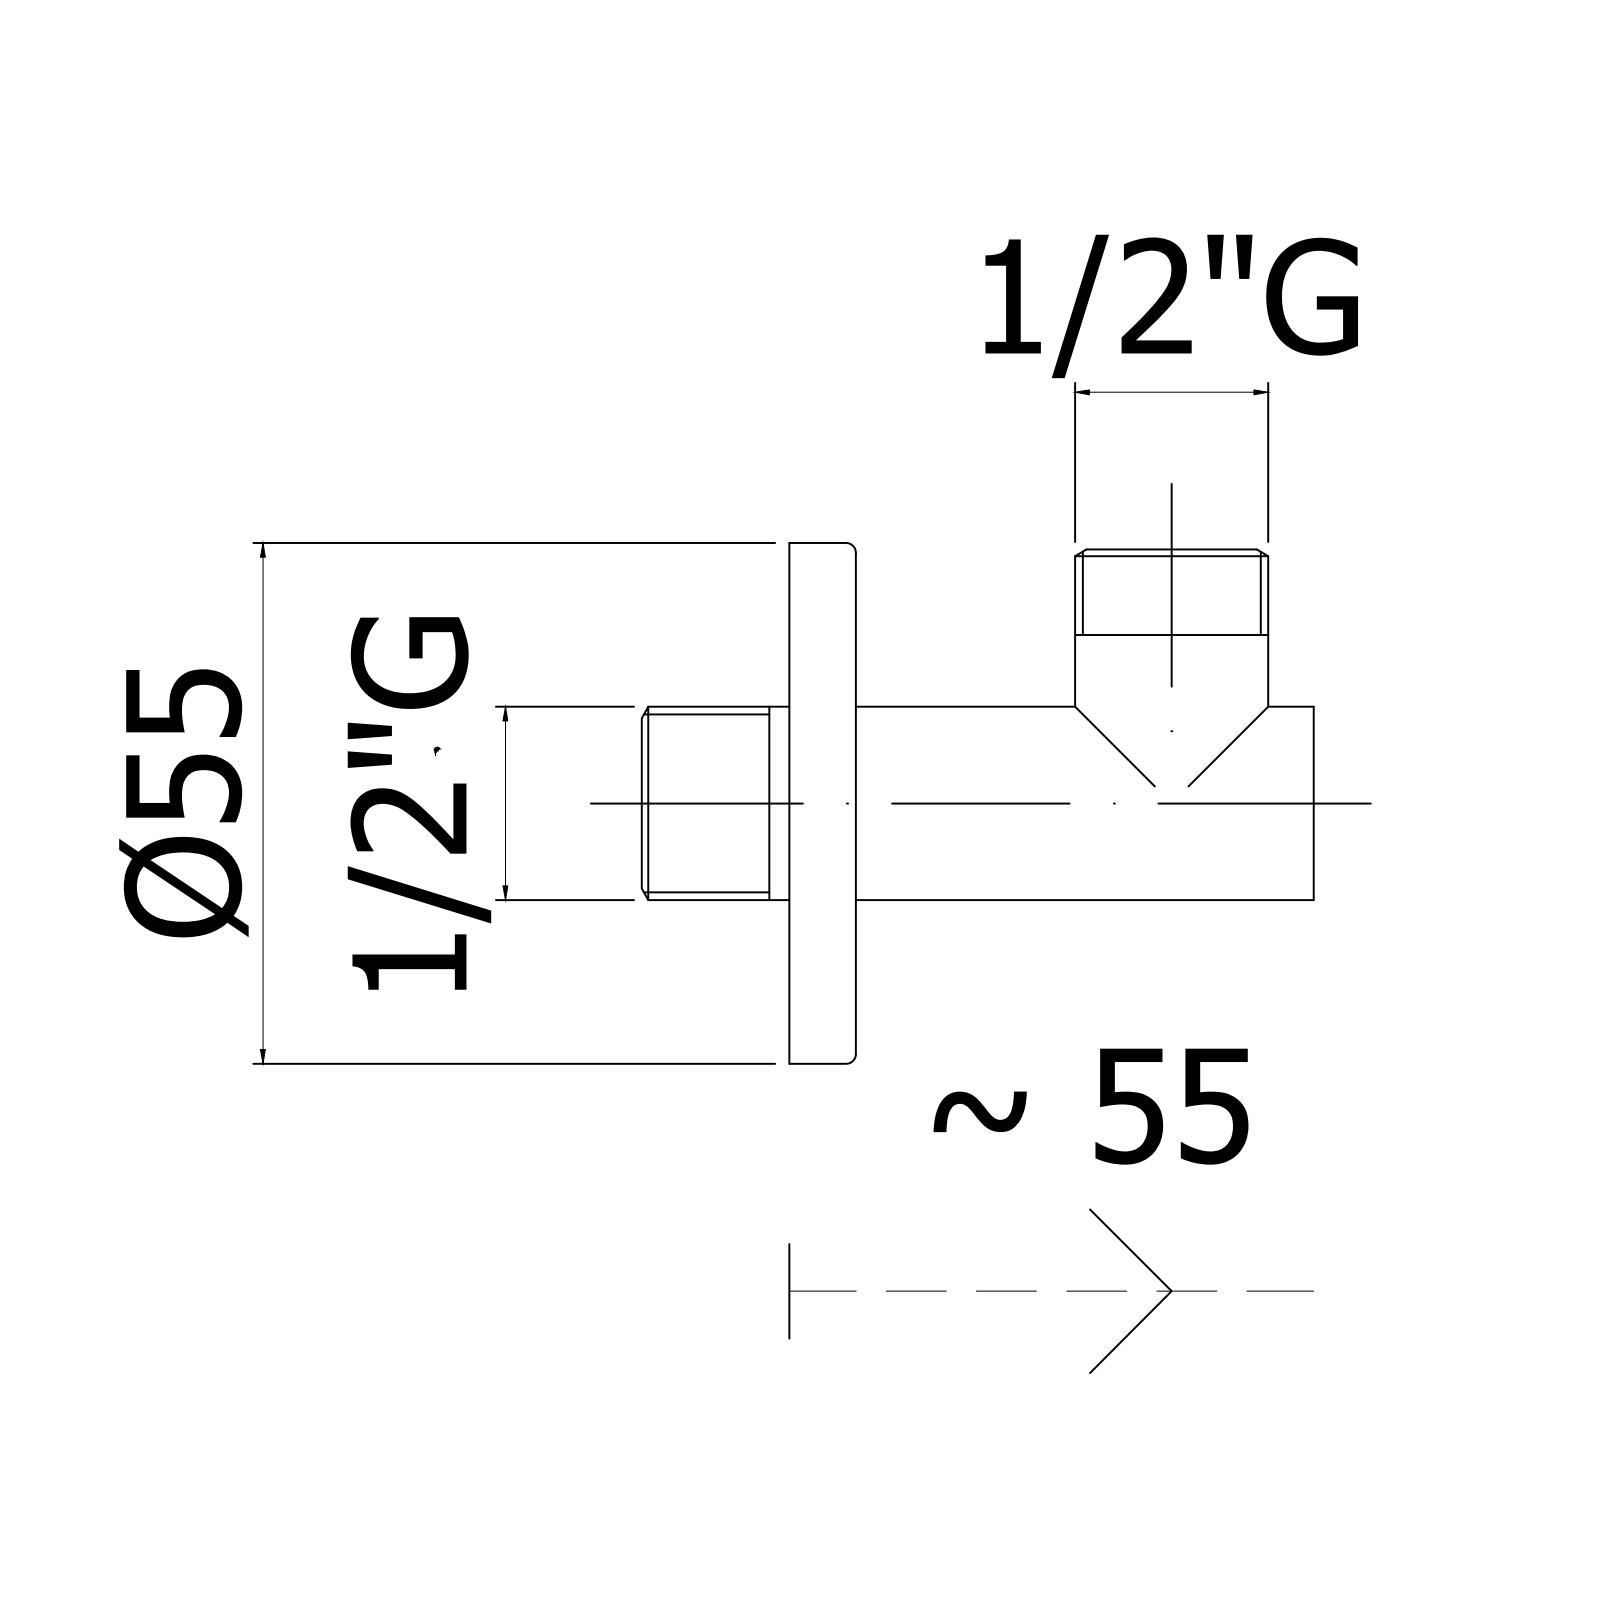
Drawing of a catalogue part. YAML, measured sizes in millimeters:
part_name: "ZACC205CR"
step_written_by: "CREO PARAMETRIC BY PTC INC, 2020044 (CONFIG_CONTROL_DESIGN)"
units: millimeters
bodies: {solids: 1, faces: 219, planar: 53, cylindrical: 72, other: 94}
overall_size: [55, 55, 46]
volume: 12638
surface_area: 14671
round_holes:
  - {diameter: 14.5, count: 1}
  - {diameter: 15.5, count: 1}
  - {diameter: 21, count: 1}
  - {diameter: 54.4, count: 1}
round_bosses_or_shafts:
  - {diameter: 20.5, count: 2}
  - {diameter: 55, count: 1}
  - {diameter: 28, count: 1}
  - {diameter: 21.6, count: 1}
partial_cylinders:
  - {radius: 0.5, count: 23}
  - {radius: 1.5, count: 2}
  - {radius: 11.25, count: 1}
  - {radius: 12.75, count: 1}
face_to_face_distances: [5.7, 6, 46, 40.3, 40, 4, 1.7, 4.3, 44.3, 3]
